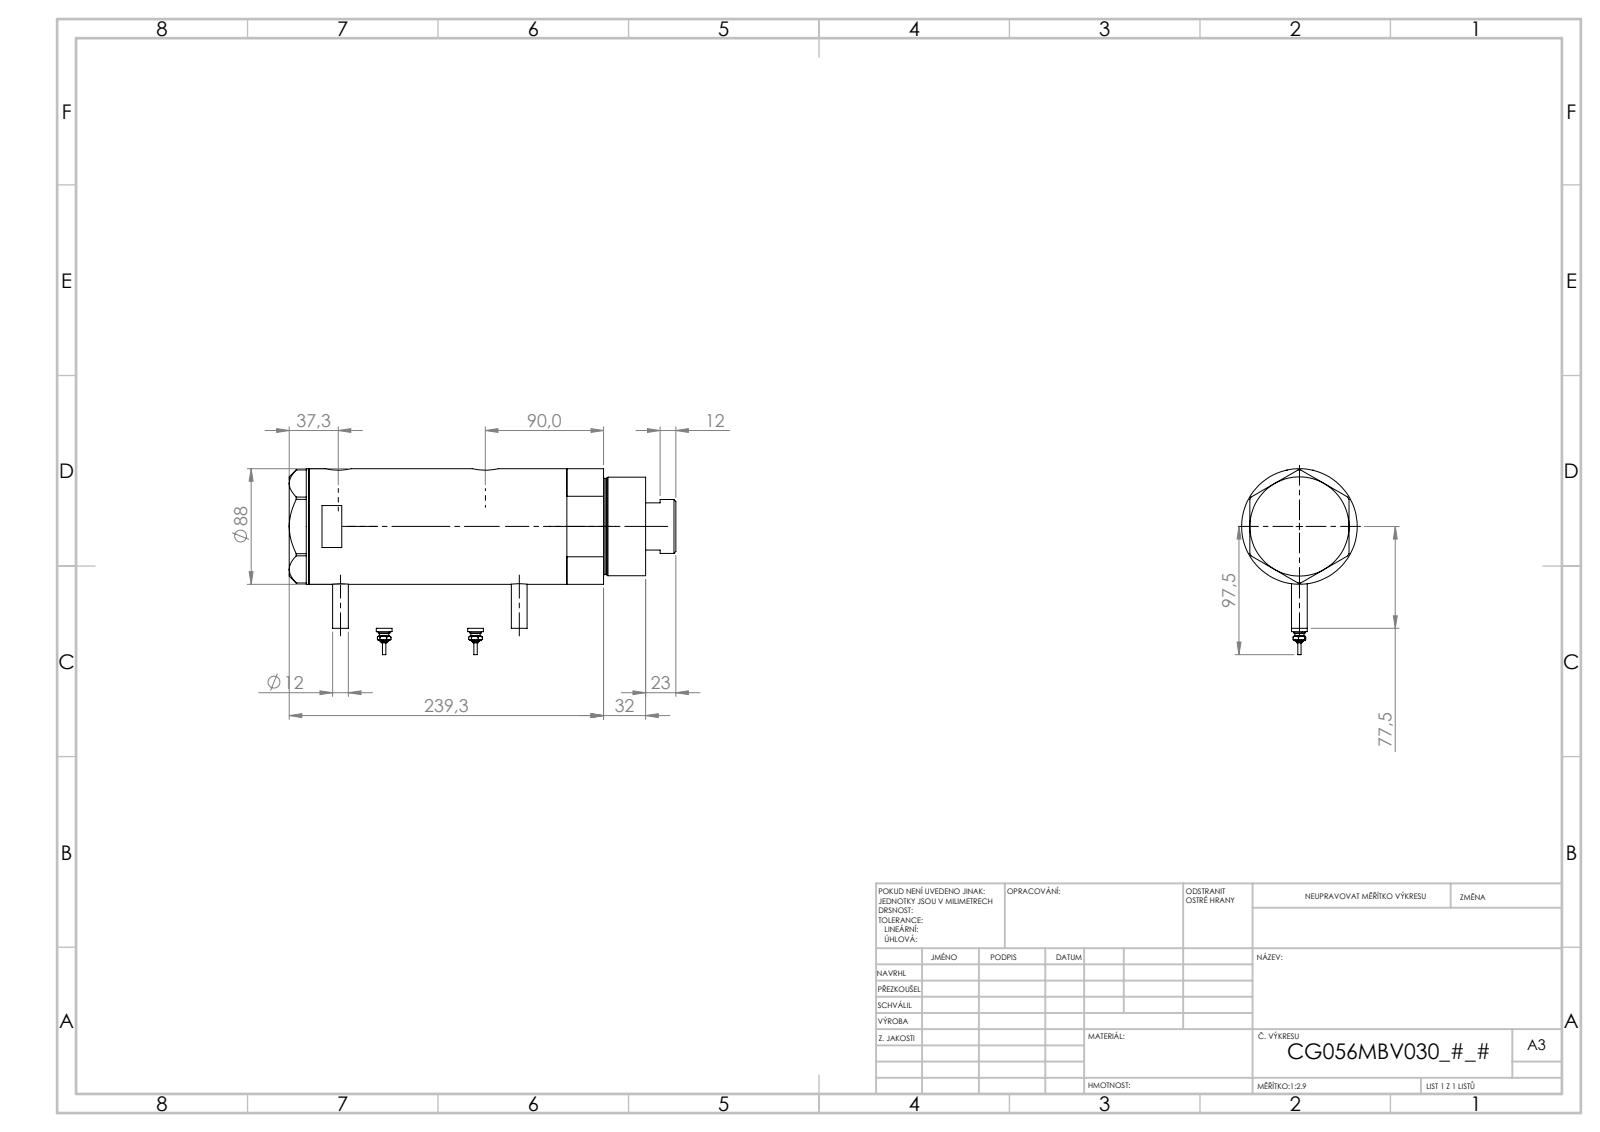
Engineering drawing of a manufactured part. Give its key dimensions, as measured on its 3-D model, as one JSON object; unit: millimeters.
{"part_name": "V270CG_VC; V270CG_BACK; V270CG_FRONT; Switch (+1 more)", "step_written_by": "SolidWorks 2019 (CONFIG_CONTROL_DESIGN)", "units": "millimeters", "bodies": {"solids": 6, "faces": 213, "planar": 80, "cylindrical": 69, "other": 64}, "overall_size": [294.3, 141.5, 88], "volume_mm3": 1563000, "surface_area_mm2": 225469, "round_holes": [[12.5, 2], [13.16, 2], [20, 2], [14.5, 1], [42, 1], [43.5, 1], [56, 1], [60, 1], [80, 1]], "round_bosses_or_shafts": [[12, 4], [9, 2], [7, 2], [4.5, 2], [2.5, 2], [88, 1], [75, 1], [73, 1]], "face_to_face_distances": [134.4, 26, 108.4, 15, 41, 149.4, 256.3, 271.3, 230.3, 121.9], "hole_center_spacings": [1.7, 25.8, 110.3, 112, 136.1, 137.8]}
